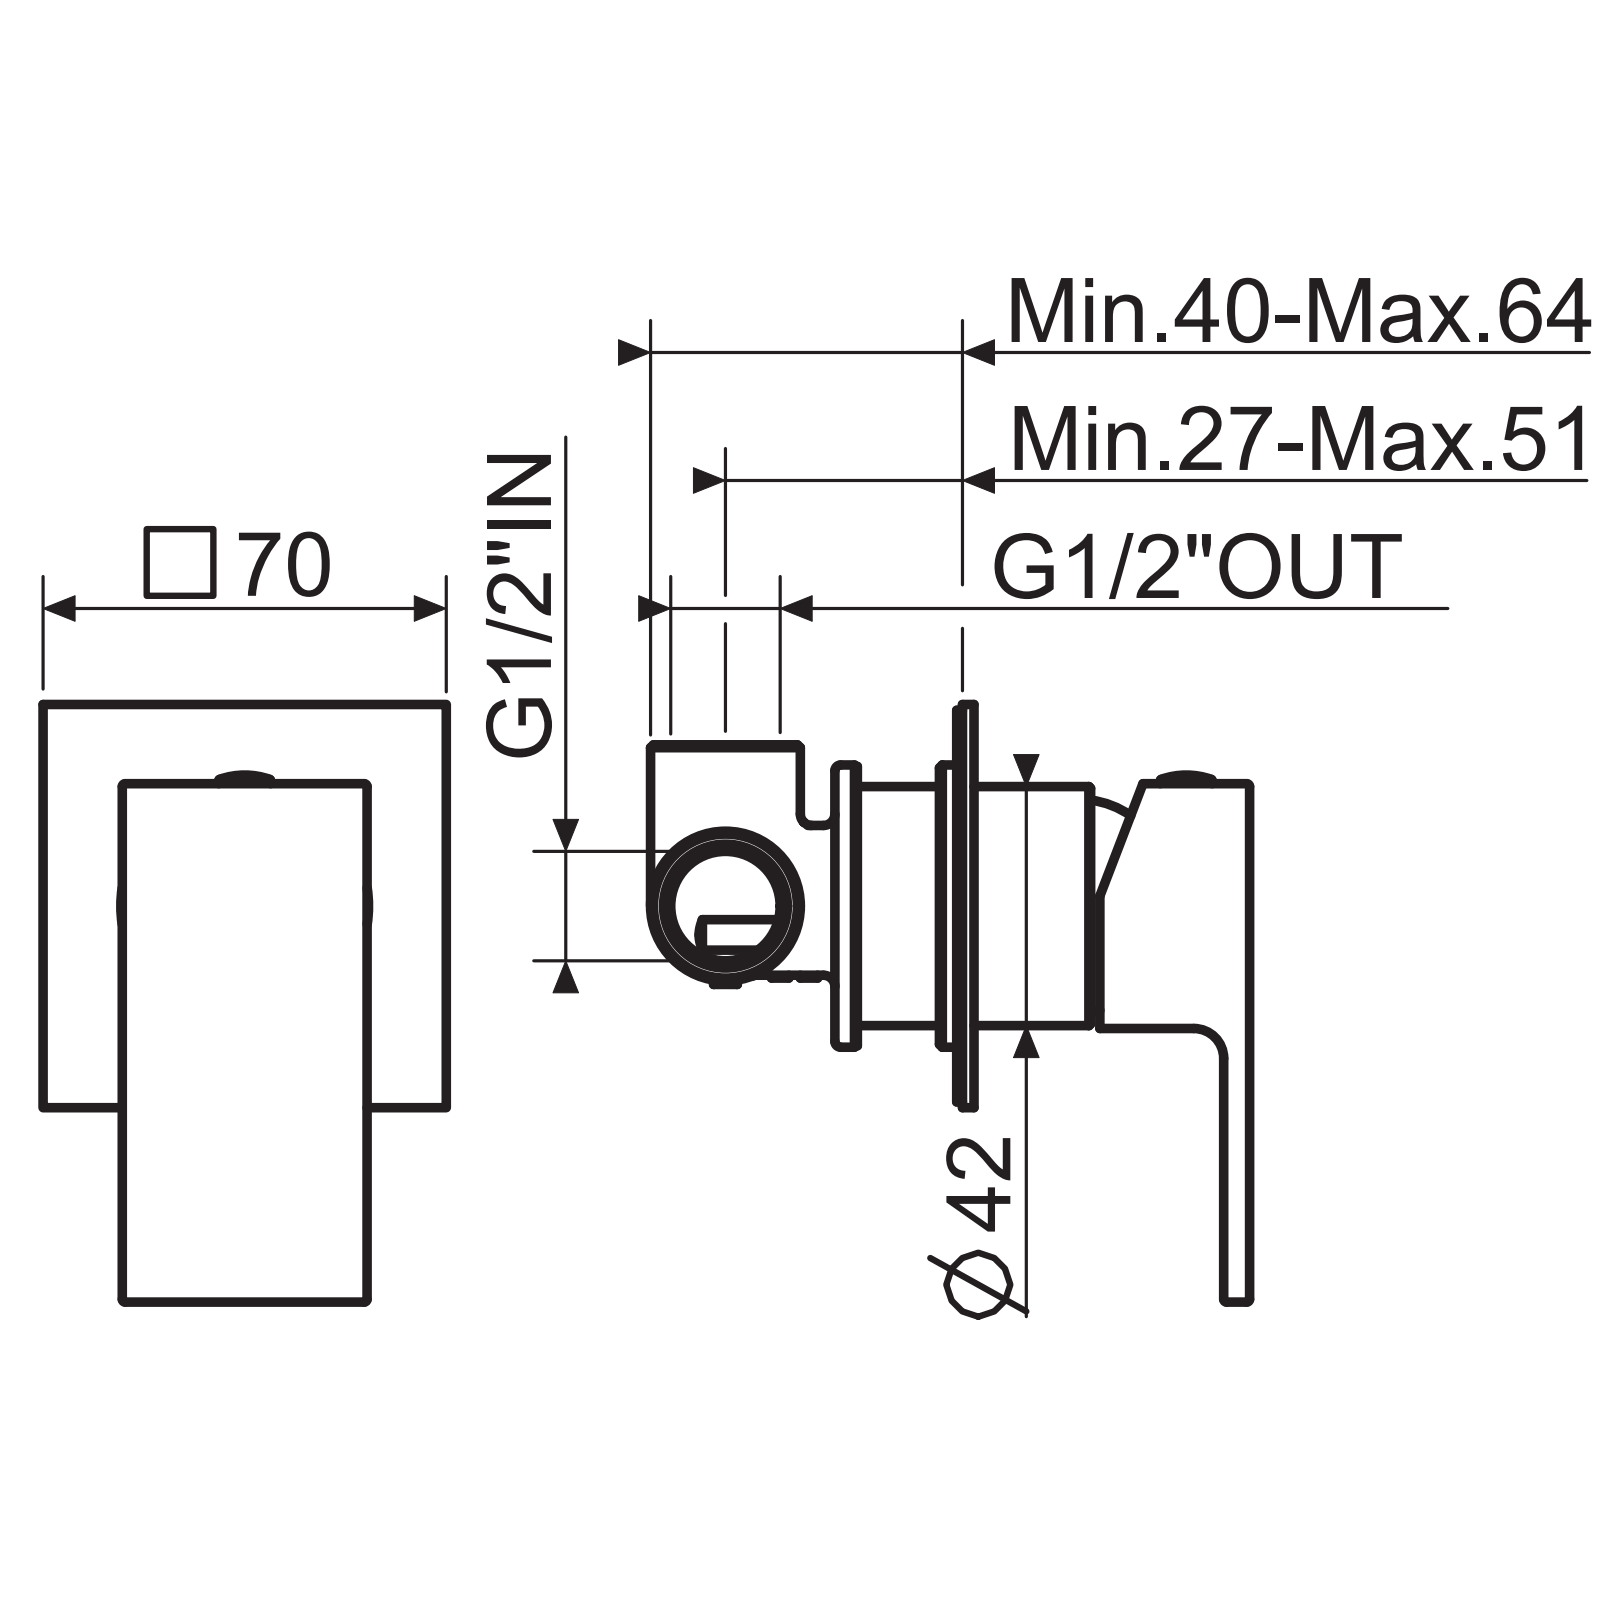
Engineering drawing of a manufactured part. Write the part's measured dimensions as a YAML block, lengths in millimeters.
part_name: "SINMAC0010_AF1; AOTT230C001; AOTT608C002_AF0; AOTT230W001_AF0 (+4 more)"
step_written_by: "CREO PARAMETRIC BY PTC INC, 2022164 (CONFIG_CONTROL_DESIGN)"
units: millimeters
bodies: {solids: 6, faces: 275, planar: 112, cylindrical: 77, other: 86}
overall_size: [103.75, 70, 50.1]
volume: 31467
surface_area: 34837
round_holes:
  - {diameter: 4.4, count: 1}
  - {diameter: 5, count: 1}
  - {diameter: 6.6, count: 1}
  - {diameter: 27.7, count: 1}
  - {diameter: 32, count: 1}
  - {diameter: 37.5, count: 1}
  - {diameter: 40, count: 1}
  - {diameter: 43, count: 1}
  - {diameter: 46.5, count: 1}
round_bosses_or_shafts:
  - {diameter: 49, count: 1}
  - {diameter: 41.5, count: 1}
  - {diameter: 36.8, count: 1}
partial_cylinders:
  - {radius: 1, count: 16}
  - {radius: 0.5, count: 13}
  - {radius: 0.3, count: 2}
  - {radius: 5.19, count: 1}
  - {radius: 20.25, count: 1}
face_to_face_distances: [2, 1.5, 49.85, 47.85, 41, 42.5, 39.5, 4.5, 45.35, 43.35]
